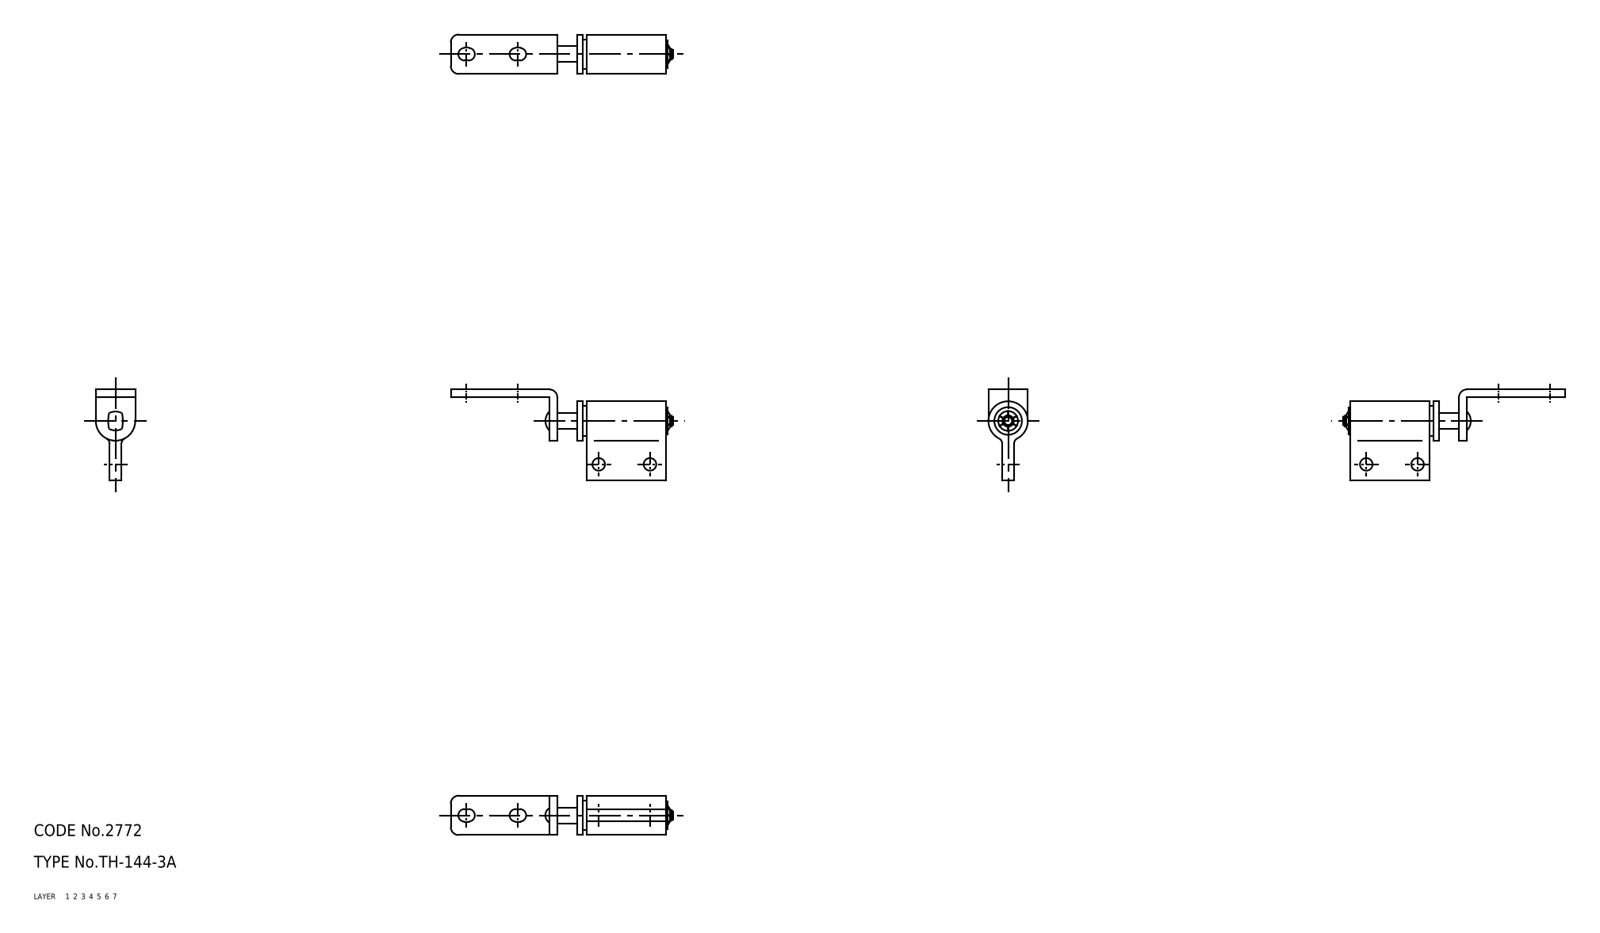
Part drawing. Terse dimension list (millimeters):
name: 67116155; 67116168; 67116181; 67116194 (+1 more)
written by: CADfix (AUTOMOTIVE_DESIGN)
unit: mm
bodies: 5 solids, 136 faces (0 planar, 0 cylindrical, 136 other)
size: 56.3 × 23 × 10
volume: 3 076 mm³; area: 3 174 mm²
